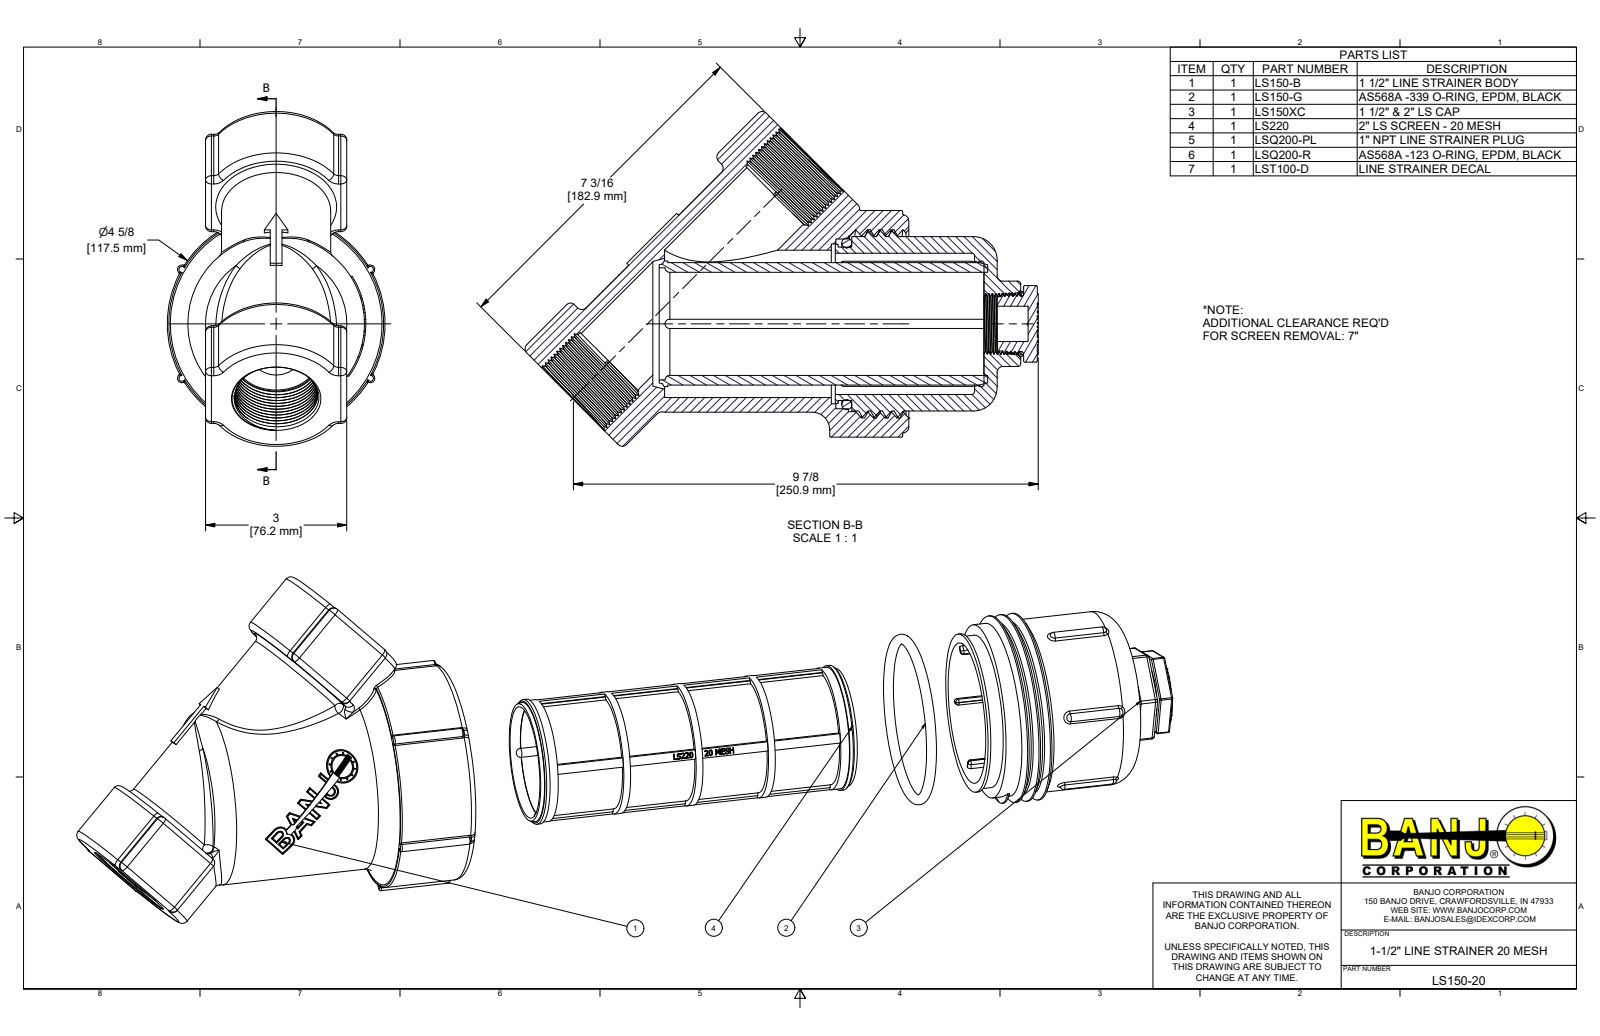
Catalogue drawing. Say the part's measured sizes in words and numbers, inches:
The part is named "LS150-B; LS150XC; LSQ200-PL; LSQ200-R (+4 more)". Its 3-D file was written by "Autodesk Inventor 2014 (AUTOMOTIVE_DESIGN)". It is 5 solids with 1428 faces: 656 planar, 262 cylindrical and 510 other. Overall it measures 10.905 by 7.102 by 4.625 inches. Its volume is 58.82 cubic inches and its surface area 482.2 square inches. Round holes: 2 of diameter 1.7, 2 of diameter 1.761, 1 of diameter 0.454, 1 of diameter 0.641, 1 of diameter 0.75, 1 of diameter 1.176, 1 of diameter 2.19, 1 of diameter 2.35, 1 of diameter 3, 1 of diameter 3.13, 1 of diameter 3.395, 1 of diameter 3.605. Round bosses or shafts: 1 of diameter 4.625, 1 of diameter 3.75, 1 of diameter 3.702, 1 of diameter 3.38, 1 of diameter 3.257, 1 of diameter 2.666, 1 of diameter 2.6, 1 of diameter 2.38. Partial cylindrical surfaces (rounded edges, fillets, slot ends): 46 of radius 0.06, 35 of radius 0.125, 30 of radius 0.03, 12 of radius 0.094, 4 of radius 0.1, 3 of radius 0.12, 2 of radius 0.065, 2 of radius 0.082. The main face-to-face distances are 1.445, 3, 7.189, 3.16, 1.595, 6.903, 3.743, 1.745, 1.34, 0.2.
